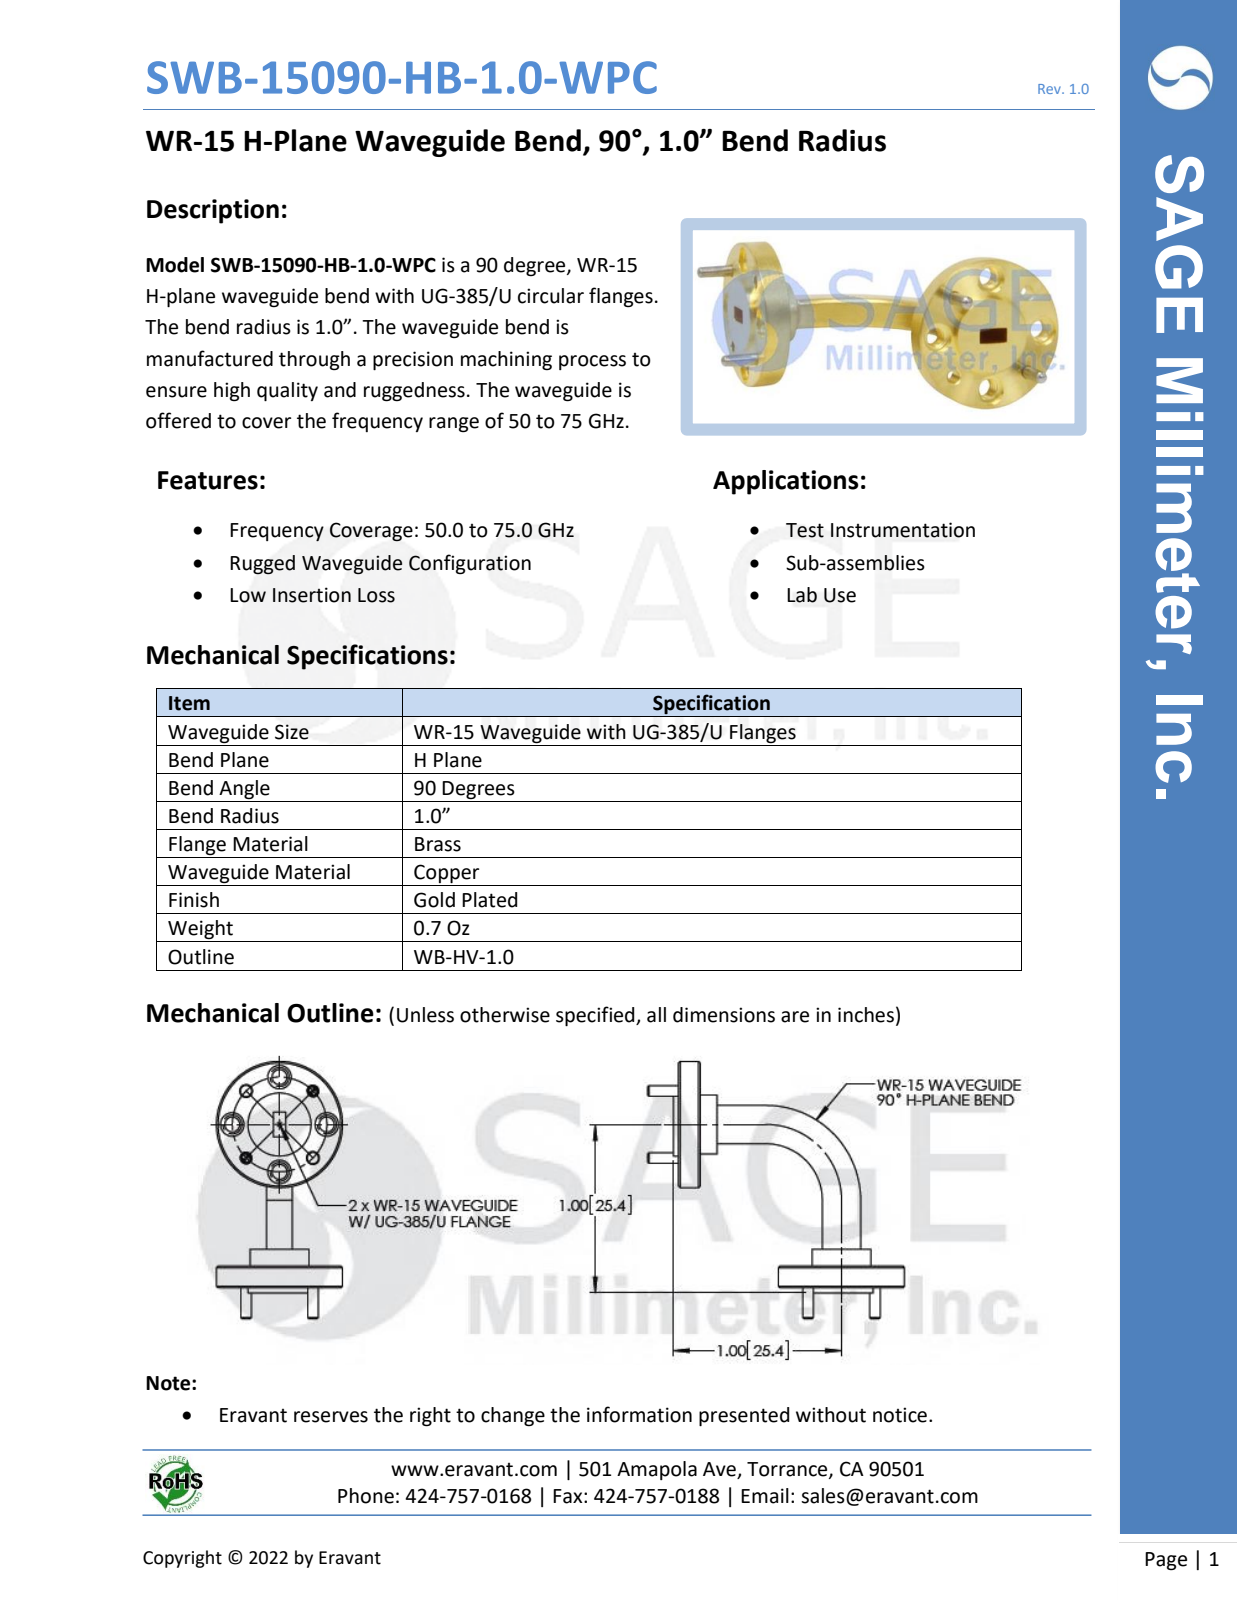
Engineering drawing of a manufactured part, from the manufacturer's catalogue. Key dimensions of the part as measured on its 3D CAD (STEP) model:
Part name (STEP PRODUCT): WB-HV-1.0, DF
STEP written by: SolidWorks 2021 (AUTOMOTIVE_DESIGN)
Units: inches
Bodies: 5 solids, 150 faces (40 planar, 70 cylindrical, 40 other)
Overall size (bounding box): 1.528 × 1.527 × 0.75
Volume: 0.178 in³ · Surface area: 4.169 in²
Round holes (diameter × count): ⌀0.089 ×8, ⌀0.14 ×8, ⌀0.06 ×4, ⌀0.067 ×4
Round bosses / shafts (diameter × count): ⌀0.063 ×4, ⌀0.75 ×2, ⌀0.35 ×2, ⌀0.375 ×1, ⌀0.375 ×1
Partial cylindrical surfaces — rounded edges, fillets, slot ends (radius × count): R0.336 ×1, R0.564 ×1
Main face-to-face distances: 0.13, 0.154, 0.03, 0.16, 0.26, 0.23, 0.1, 0.02, 0.886, 1.114
Hole centre spacings: 0.215, 0.398, 0.519, 0.562
